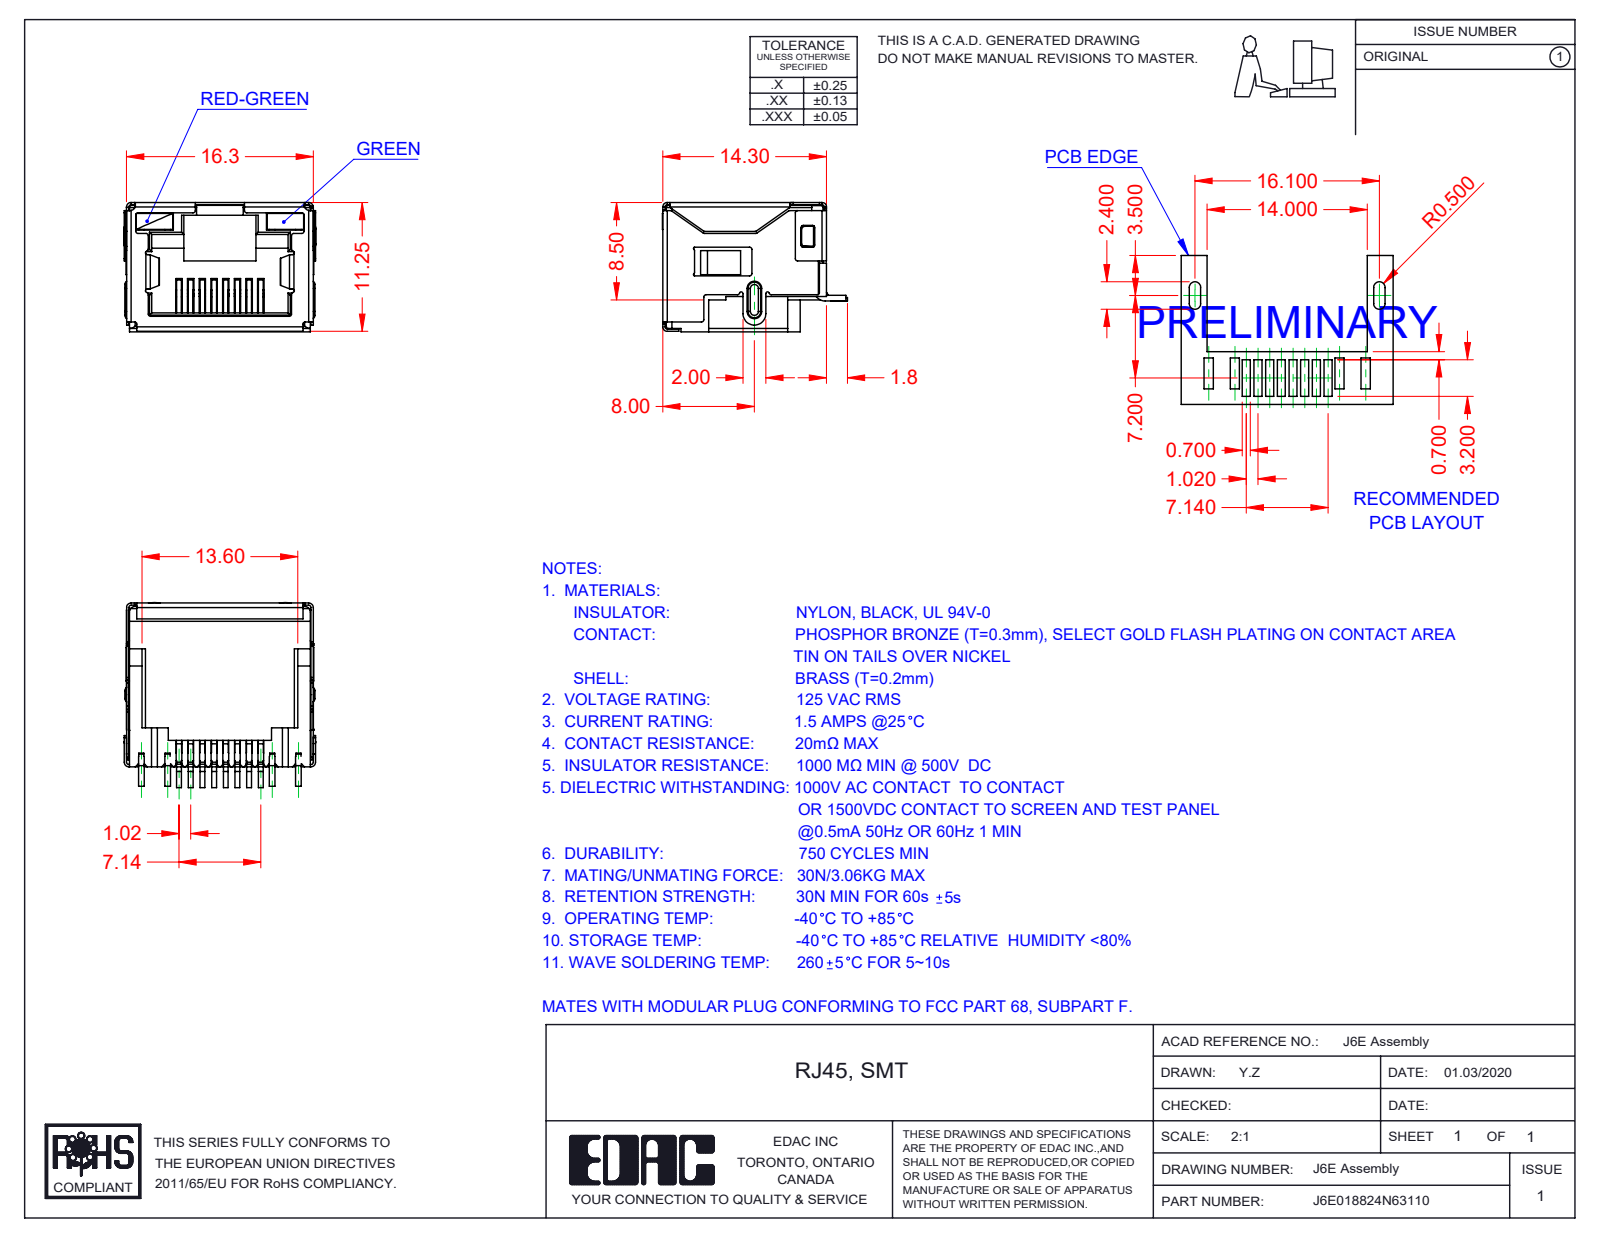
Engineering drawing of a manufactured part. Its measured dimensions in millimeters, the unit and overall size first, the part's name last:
Units: millimetres
Overall size (bounding box): 16.75 × 16.15 × 11.3
Partial cylindrical surfaces — rounded edges, fillets, slot ends (radius × count): R0.2 ×82, R0.25 ×17, R0.4 ×13, R0.5 ×13, R0.1 ×10, R0.15 ×7, R0.3 ×4, R1 ×3
Main face-to-face distances: 11.05, 16.05, 16.1, 15.85, 11.1, 11.3, 2.4, 0.7, 9.85, 0.49
Volume: 1 109 mm³ · Surface area: 4 045 mm²
Bodies: 12 solids, 1498 faces (1099 planar, 349 cylindrical, 50 other)
Part name (STEP PRODUCT): 6E LED RH_3-Green; 6E Shield_LED; 6E LED LH_6-Red-Green; 6E Insulator_LED (+2 more)
STEP written by: SolidWorks 2016 (CONFIG_CONTROL_DESIGN)
